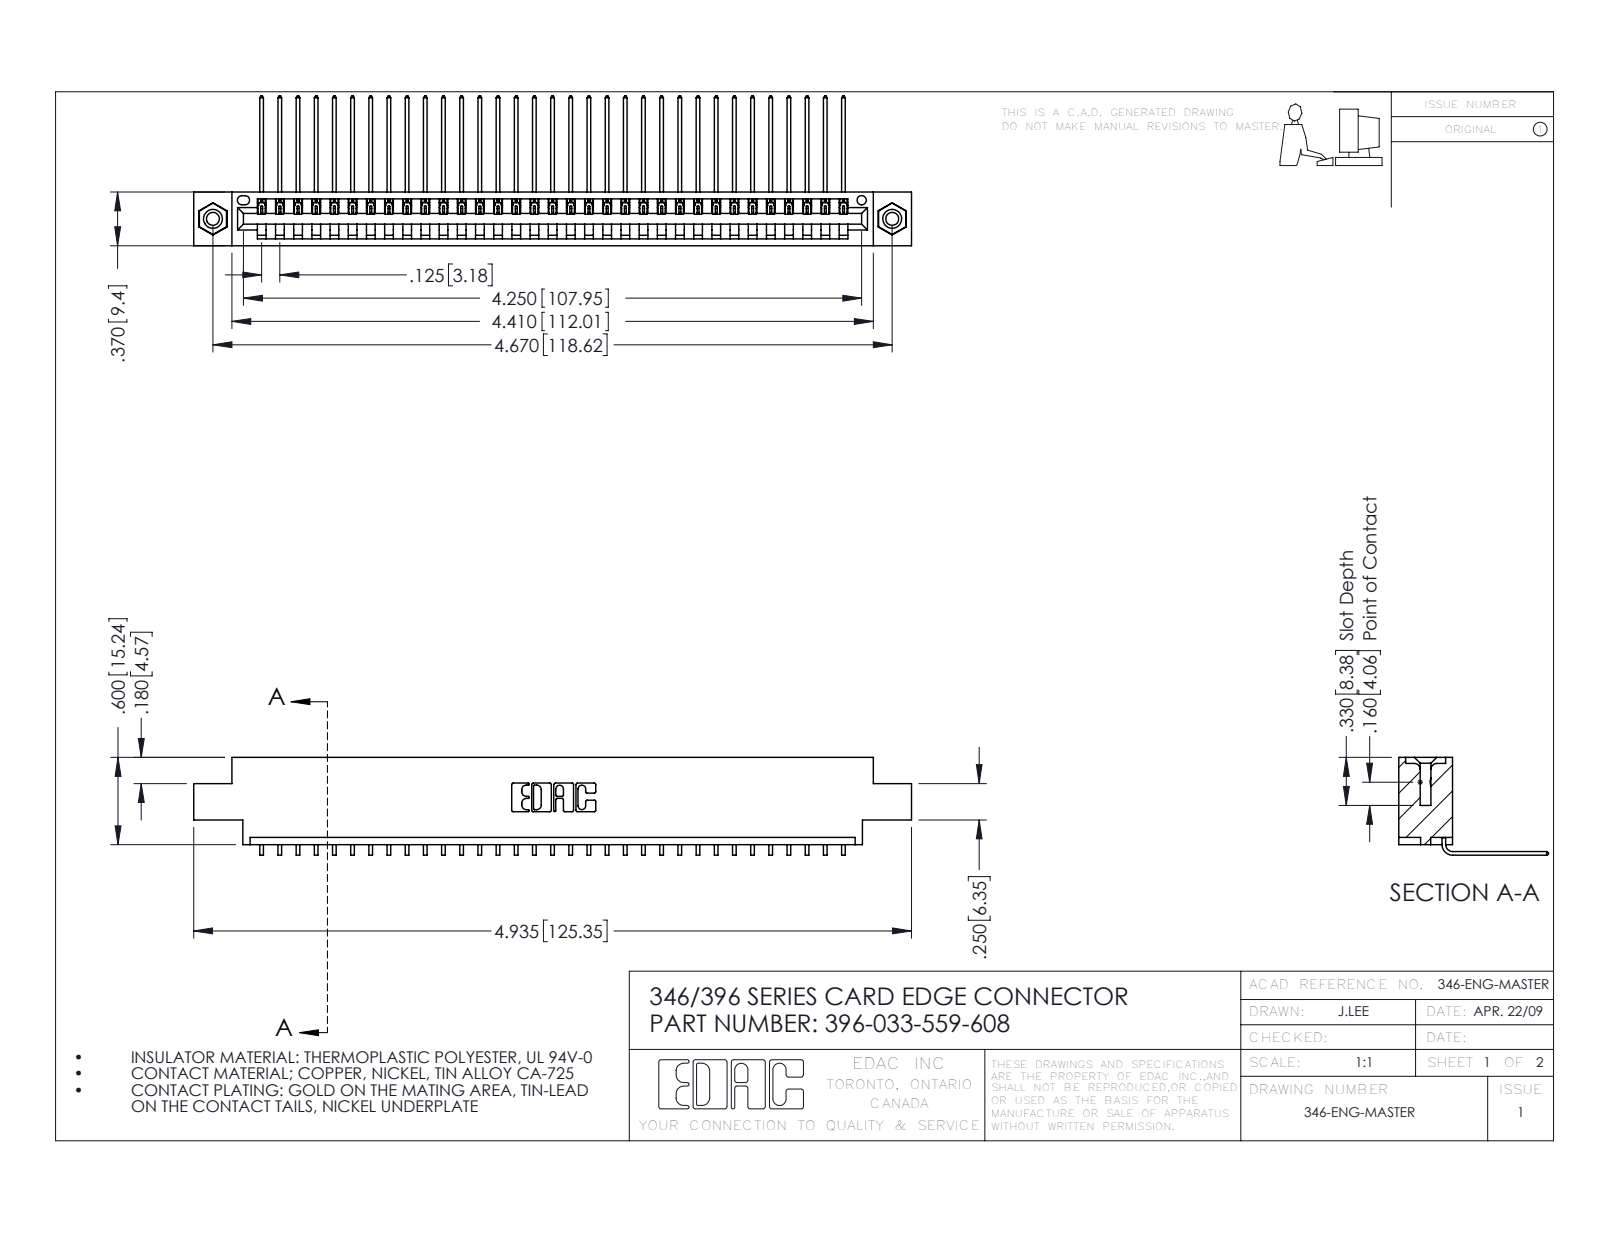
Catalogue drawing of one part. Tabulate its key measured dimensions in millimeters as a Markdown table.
| quantity | value |
| --- | --- |
| part name | 345-292-001_558 559 Tail - 1; 346 Part_0.170 Offset - 0.156 Dia-TI; 396-033-559-608; 345-250-001_345-250-003-102 |
| STEP written by | SolidWorks 2016 (CONFIG_CONTROL_DESIGN) |
| units | millimeters |
| bodies | 36 solids, 2166 faces (1498 planar, 652 cylindrical, 16 other) |
| overall size | 125.3 × 26.2 × 17.1 |
| volume | 11 900 mm³ |
| surface area | 15 590 mm² |
| round holes (diameter × count) | 2.3 × 2, 3.2 × 2, 4 × 2, 1.6 × 1 |
| round bosses / shafts (diameter × count) | 3.9 × 2 |
| partial cylindrical surfaces (radius × count) | 0.2 × 66, 0.3 × 22, 0.2 × 6, 0.8 × 6, 0.7 × 3, 0.8 × 2, 1 × 2, 0.4 × 1 |
| main face-to-face distances | 1.2, 8.2, 9.4, 0.6, 6.4, 1.8, 5.6, 3.8, 7.6, 2.5 |
| hole center spacings | 6.2, 113.3, 118.6 |
